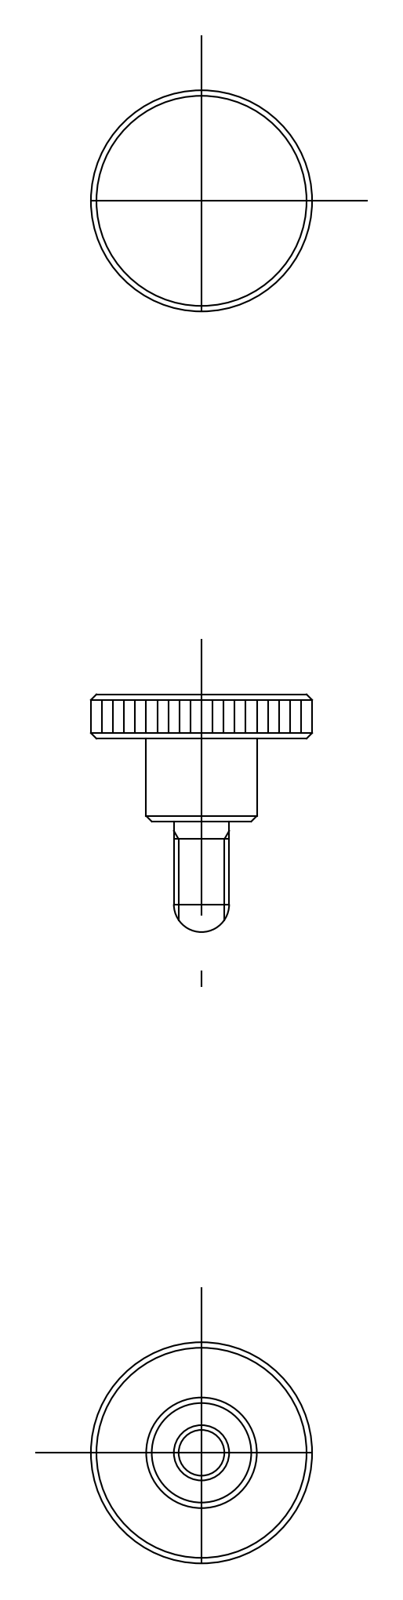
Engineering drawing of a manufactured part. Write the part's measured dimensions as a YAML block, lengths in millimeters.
part_name: "knob"
step_written_by: "CADfix (AUTOMOTIVE_DESIGN)"
units: millimeters
bodies: {solids: 1, faces: 16, planar: 0, cylindrical: 0, other: 16}
overall_size: [21.5, 20, 20]
volume: 2010
surface_area: 1206
